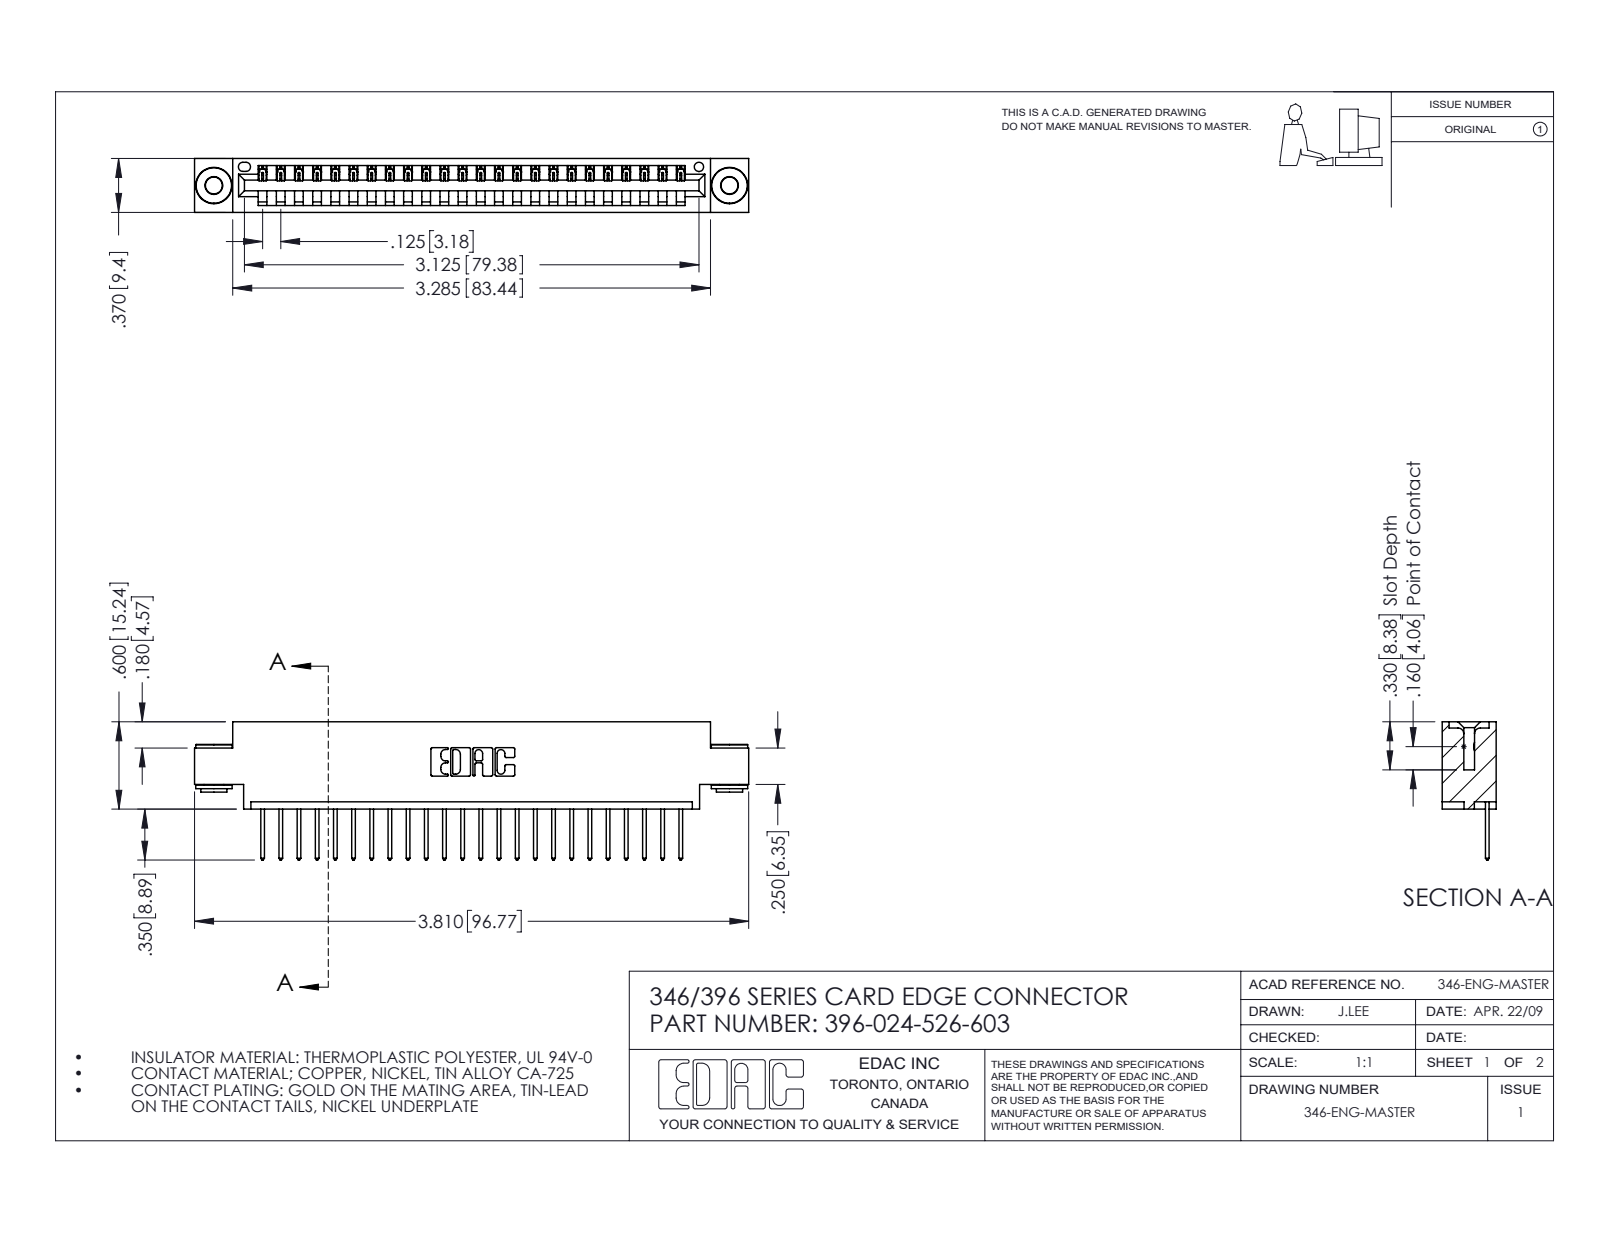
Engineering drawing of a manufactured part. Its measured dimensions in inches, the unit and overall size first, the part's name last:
Units: inches
Overall size (bounding box): 3.81 × 0.95 × 0.37
Round holes (diameter × count): ⌀0.116 ×2, ⌀0.156 ×2, ⌀0.064 ×1
Round bosses / shafts (diameter × count): ⌀0.25 ×2, ⌀0.18 ×2, ⌀0.136 ×2
Partial cylindrical surfaces — rounded edges, fillets, slot ends (radius × count): R0.006 ×48, R0.01 ×48, R0.01 ×22, R0.007 ×6, R0.031 ×6, R0.026 ×3, R0.031 ×2, R0.04 ×2
Main face-to-face distances: 0.048, 0.322, 0.37, 0.25, 0.025, 0.072, 0.298, 0.148, 0.222, 0.1
Hole centre spacings: 0.246, 3.337, 3.545
Volume: 0.548 in³ · Surface area: 17.66 in²
Bodies: 27 solids, 1556 faces (1050 planar, 498 cylindrical, 8 other)
Part name (STEP PRODUCT): 346 Part_0.170 Offset - 0.156 Dia-TH; 396-024-526-603; 345-250-002_345-250-002-102; 345-292-001_345-293-126
STEP written by: SolidWorks 2016 (CONFIG_CONTROL_DESIGN)
